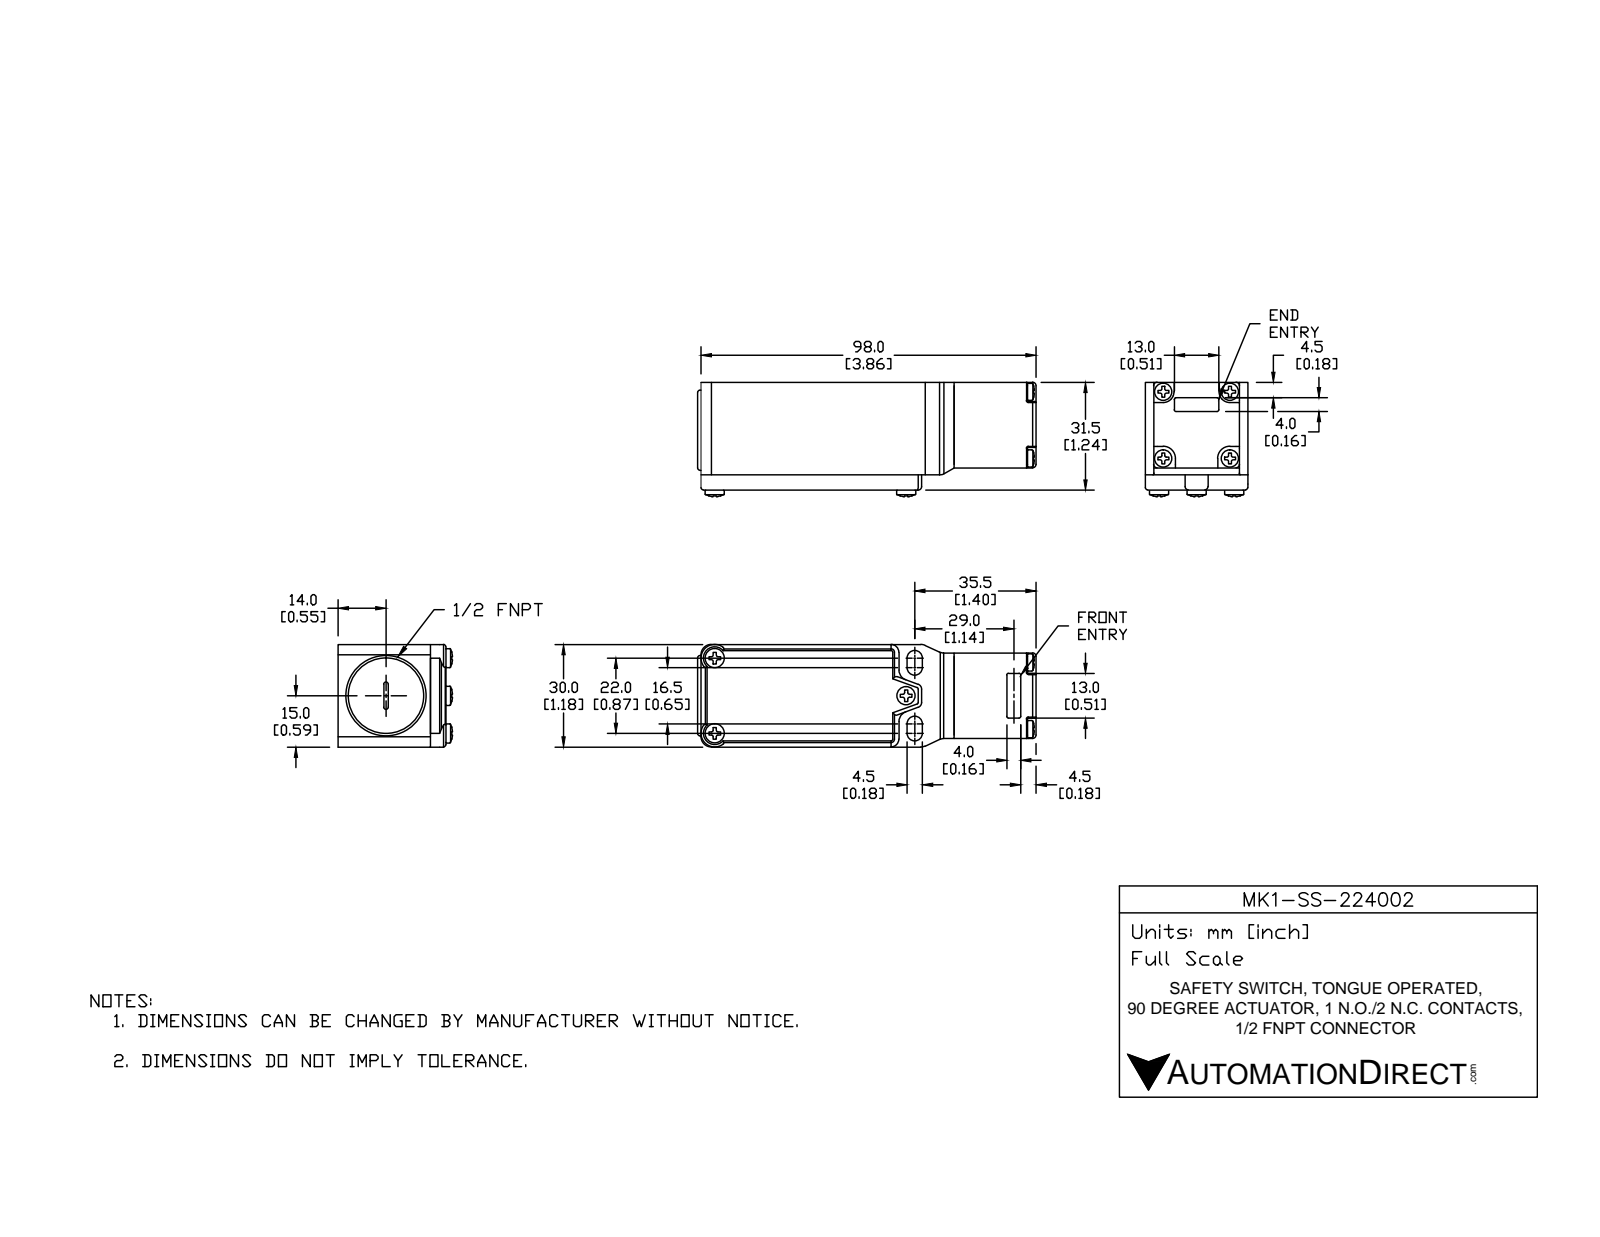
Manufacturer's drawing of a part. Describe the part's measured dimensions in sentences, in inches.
The part is named "MK1-SS-224002". Its 3-D file was written by "SolidWorks 2014 (AUTOMOTIVE_DESIGN)". It is 12 solids with 1178 faces: 346 planar, 474 cylindrical and 358 other. Overall it measures 3.898 by 1.317 by 1.181 inches. Its volume is 2.278 cubic inches and its surface area 48.69 square inches. Round holes: 8 of diameter 0.098, 7 of diameter 0.126, 3 of diameter 0.157, 2 of diameter 0.059, 2 of diameter 0.071, 2 of diameter 0.087, 2 of diameter 0.142, 1 of diameter 0.114, 1 of diameter 0.173, 1 of diameter 0.217, 1 of diameter 0.406, 1 of diameter 0.535. Round bosses or shafts: 7 of diameter 0.118, 5 of diameter 0.197, 4 of diameter 0.138, 3 of diameter 0.22, 1 of diameter 0.925, 1 of diameter 0.697, 1 of diameter 0.236. Partial cylindrical surfaces (rounded edges, fillets, slot ends): 159 of radius 0.02, 58 of radius 0.012, 24 of radius 0.039, 14 of radius 0.006, 8 of radius 0.028, 8 of radius 0.031, 8 of radius 0.118, 4 of radius 0.089. The main face-to-face distances are 0.098, 0.079, 1.142, 0.114, 1.067, 1.181, 1.24, 0.177, 0.039, 0.969. The hole center spacings are 0.543, 0.768, 0.187, 0.423, 0.426, 0.476, 0.503, 0.581.
